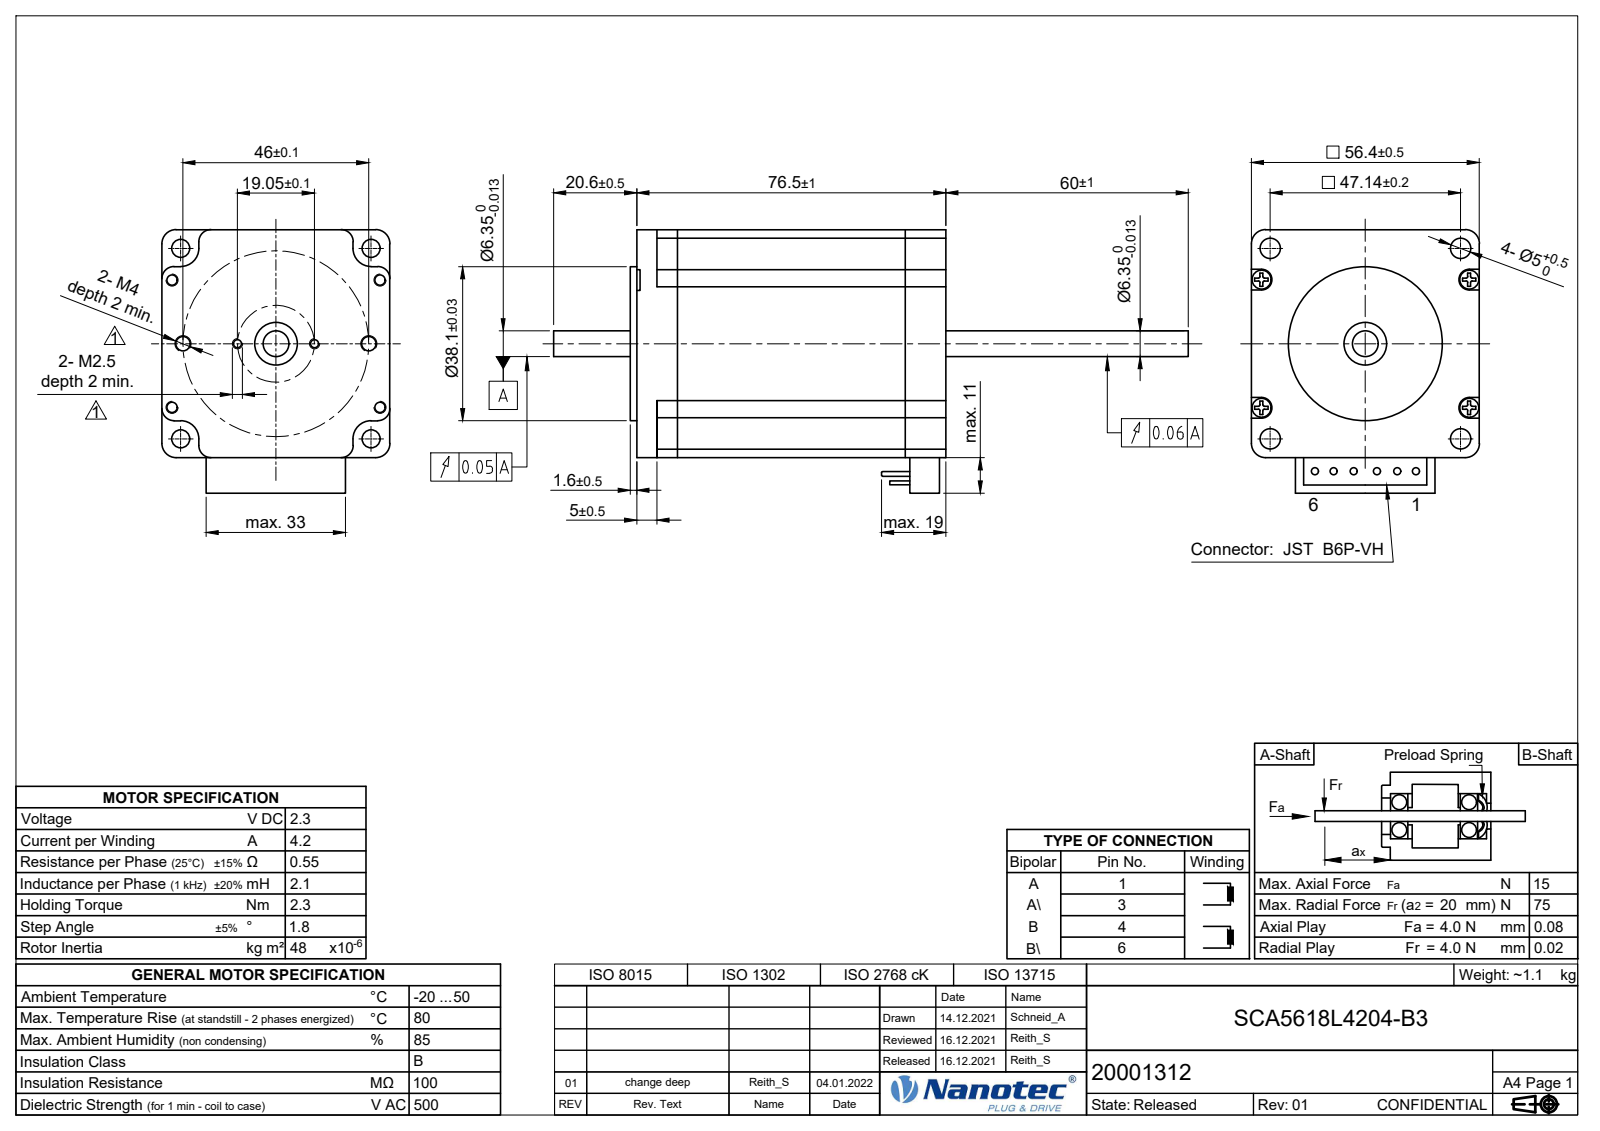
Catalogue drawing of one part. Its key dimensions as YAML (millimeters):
part_name: "SCA5618L-B3_Shrinkwrap_1"
step_written_by: "Autodesk Inventor 2019 (AUTOMOTIVE_DESIGN)"
units: millimeters
bodies: {solids: 4, faces: 178, planar: 109, cylindrical: 58, other: 11}
overall_size: [157.1, 66.9, 56.54]
volume: 228101
surface_area: 40347
round_holes:
  - {diameter: 2.5, count: 4}
  - {diameter: 3.2, count: 4}
  - {diameter: 5, count: 4}
  - {diameter: 2.01, count: 2}
  - {diameter: 3.24, count: 2}
  - {diameter: 2, count: 1}
  - {diameter: 8.2, count: 1}
  - {diameter: 10.5, count: 1}
round_bosses_or_shafts:
  - {diameter: 5.6, count: 4}
  - {diameter: 38.1, count: 1}
  - {diameter: 6.35, count: 1}
partial_cylinders:
  - {radius: 2.3, count: 12}
  - {radius: 2, count: 8}
  - {radius: 3.2, count: 4}
  - {radius: 5, count: 4}
face_to_face_distances: [60, 56.4, 71.5, 11.5, 5, 65, 76.5, 9.2, 47.2, 1.6]
hole_center_spacings: [7.94, 16.05, 22.49, 23.58, 27.43, 30, 33.33, 38.43]
